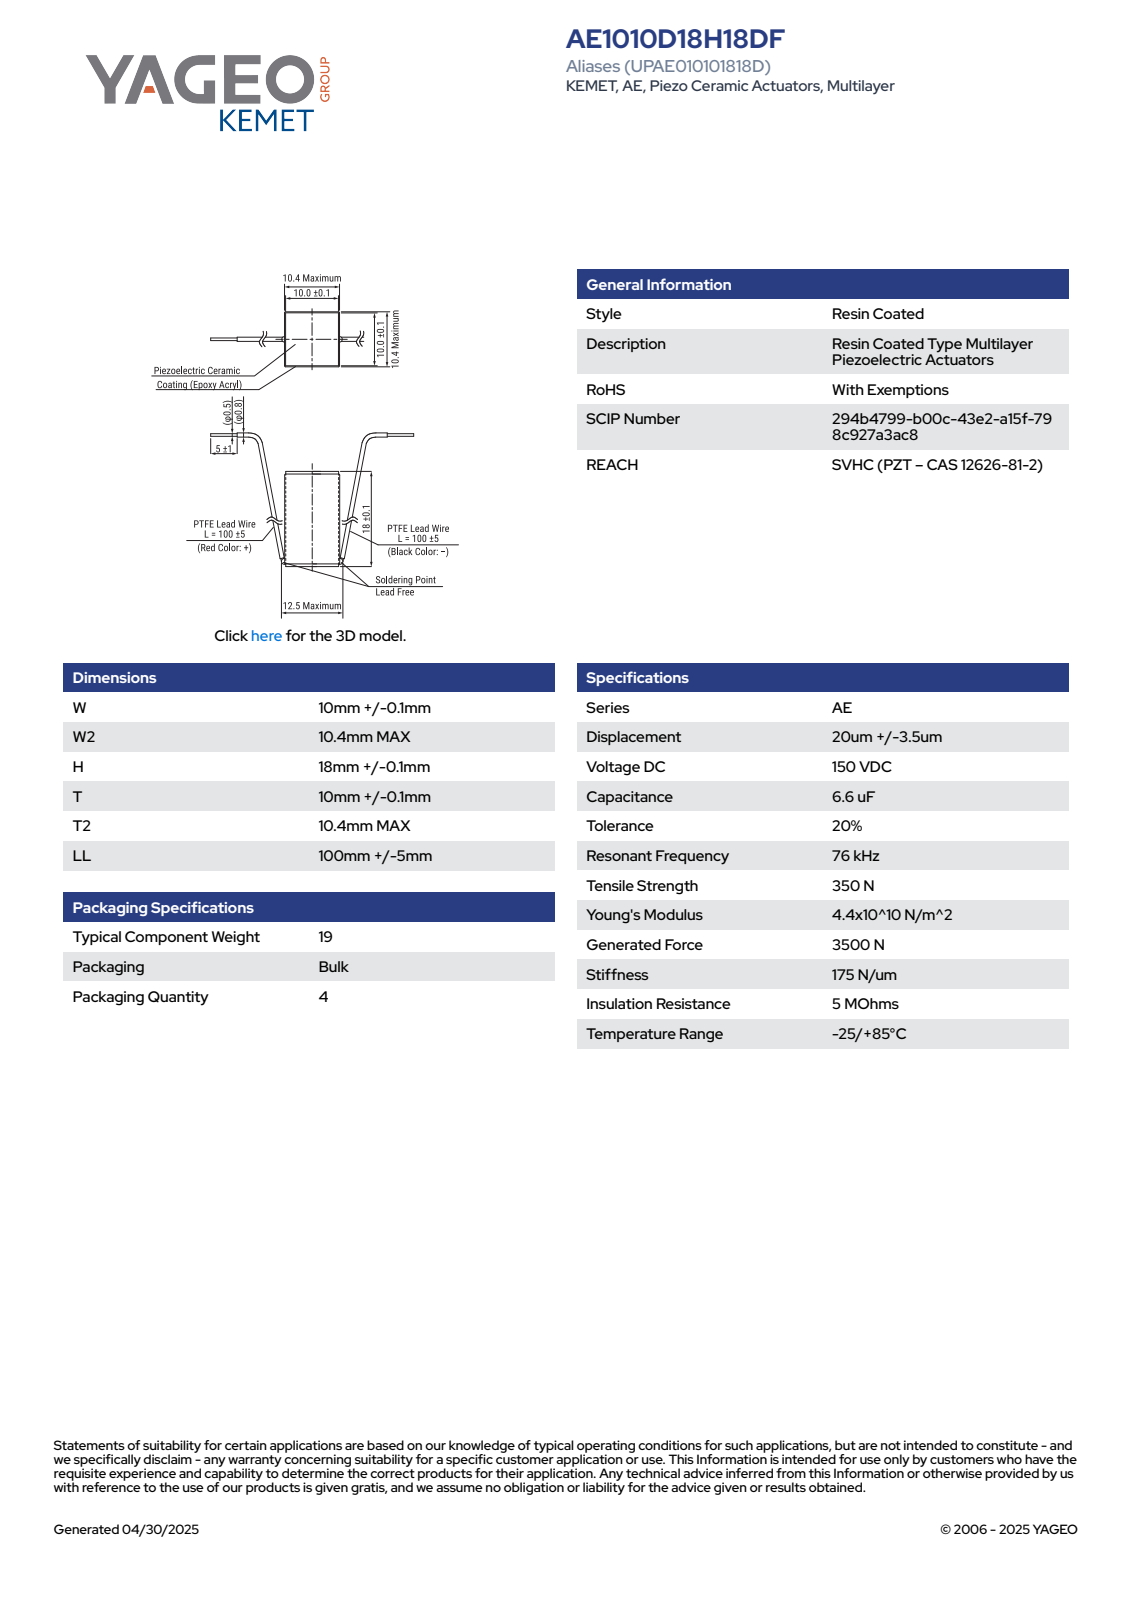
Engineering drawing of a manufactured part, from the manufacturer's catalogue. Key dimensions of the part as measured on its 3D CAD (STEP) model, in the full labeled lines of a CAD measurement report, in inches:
Part name (STEP PRODUCT): AL_KAE1_W10.1W210.4H18.1T10.1T210.4
STEP written by: SolidWorks 2014 (AUTOMOTIVE_DESIGN)
Units: inches
Bodies: 4 solids, 93 faces (85 planar, 8 cylindrical, 0 other)
Overall size (bounding box): 0.713 × 0.409 × 0.409
Volume: 0.113 in³ · Surface area: 1.51 in²
Partial cylindrical surfaces — rounded edges, fillets, slot ends (radius × count): R0.006 ×8
Main face-to-face distances: 0.398, 0.404, 0.394, 0.39, 0.713, 0.409, 0.07, 0.643, 0.287, 0.426
